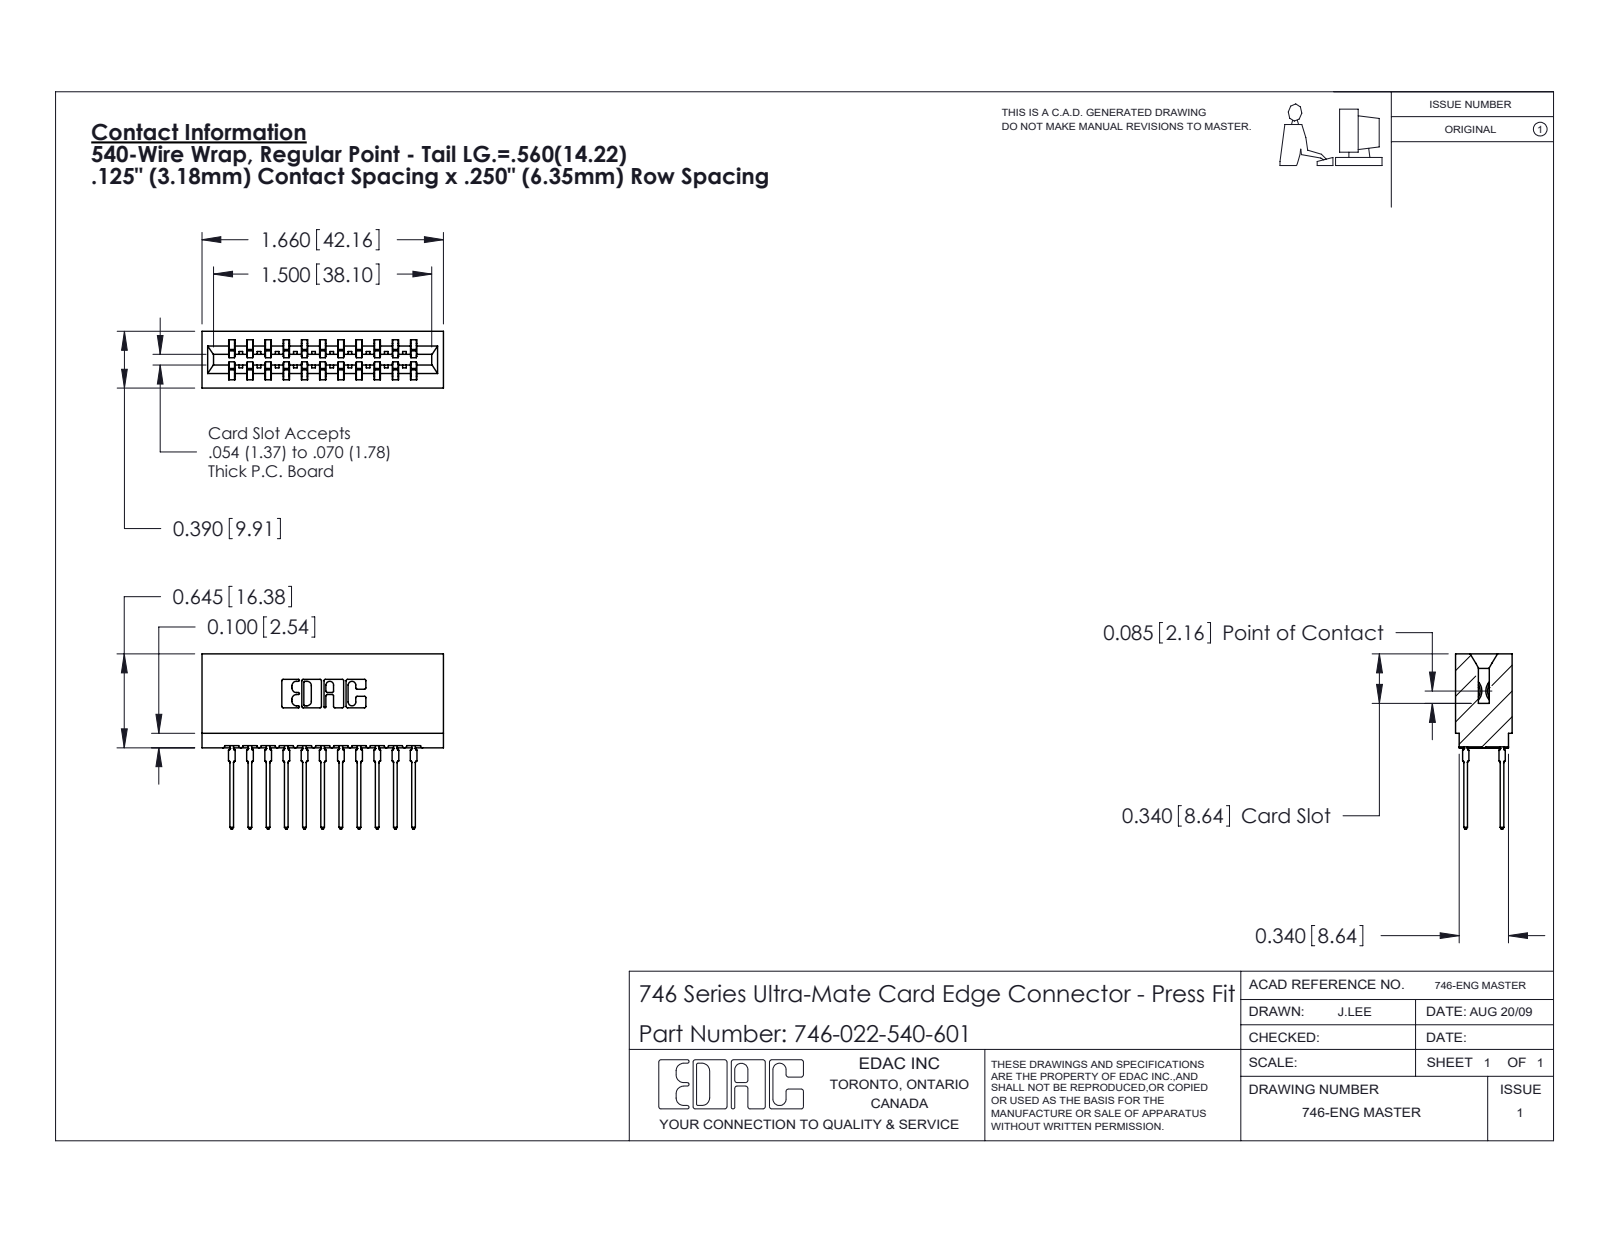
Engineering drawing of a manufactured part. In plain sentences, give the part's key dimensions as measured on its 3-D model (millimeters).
The part is named "746-022-540-601; 746 Part_.340 Slot Depth - 01; 746-292-001_540". Its 3-D file was written by "SolidWorks 2020 (CONFIG_CONTROL_DESIGN)". It is 23 solids with 2066 faces: 1067 planar, 427 cylindrical and 572 other. Overall it measures 42.2 by 30.6 by 9.9 millimeters. Its volume is 5 100 cubic millimeters and its surface area 7 213 square millimeters. Partial cylindrical surfaces (rounded edges, fillets, slot ends): 44 of radius 0.5, 22 of radius 0.3, 12 of radius 0.4, 8 of radius 0.1, 8 of radius 0.3, 6 of radius 0.2, 6 of radius 0.8, 3 of radius 0.7. The main face-to-face distances are 6.4, 1.4, 8.5, 12.7, 3.2, 7.4, 3.2, 1.1, 13.8, 2.1.
